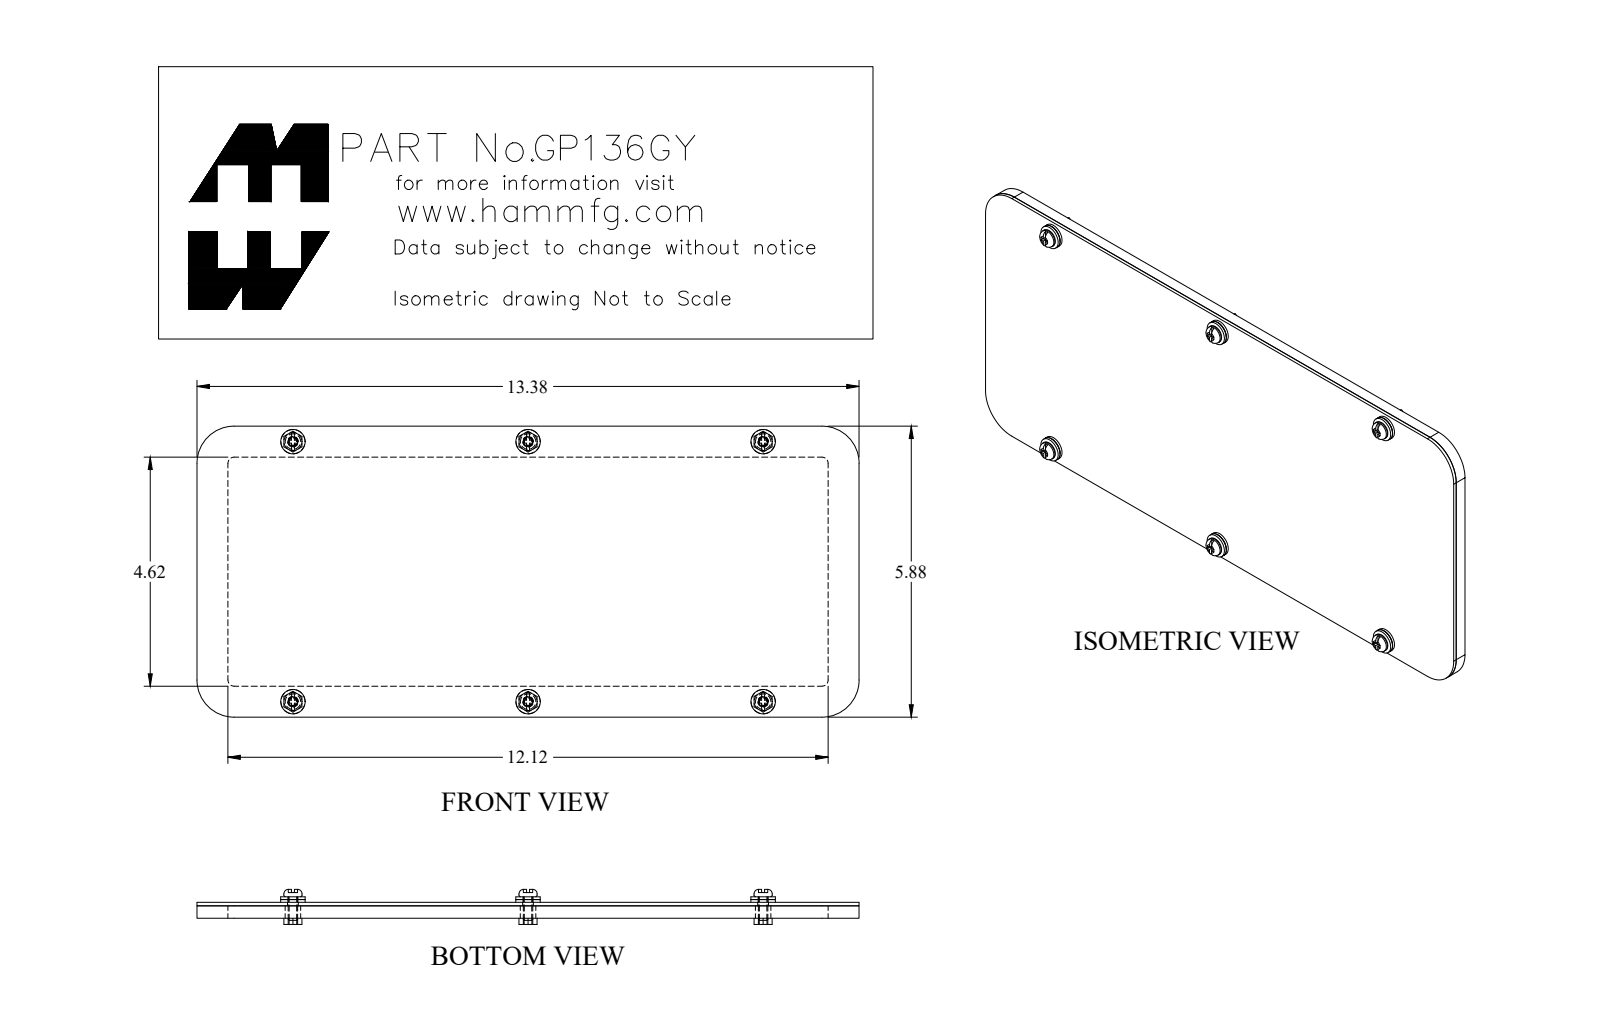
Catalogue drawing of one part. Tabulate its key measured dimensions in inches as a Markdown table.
| quantity | value |
| --- | --- |
| part name | GP136GY |
| STEP written by | SolidWorks 2018 (AUTOMOTIVE_DESIGN) |
| units | inches |
| bodies | 20 solids, 346 faces (190 planar, 120 cylindrical, 36 other) |
| overall size | 13.375 × 5.875 × 0.707 |
| volume | 11.33 in³ |
| surface area | 230.8 in² |
| round holes (diameter × count) | 0.156 × 6, 0.197 × 6, 0.218 × 6, 0.313 × 6 |
| round bosses / shafts (diameter × count) | 0.494 × 6, 0.488 × 6, 0.367 × 6, 0.19 × 6 |
| partial cylindrical surfaces (radius × count) | 0.125 × 4, 0.75 × 4 |
| main face-to-face distances | 0.072, 0.322, 0.25, 0.625, 5.25, 5.875, 4.625, 12.75, 13.375, 0.11 |
| hole center spacings | 4.75, 7.08, 9.499, 5.25, 7.08, 7.08, 10.854, 4.749 |
